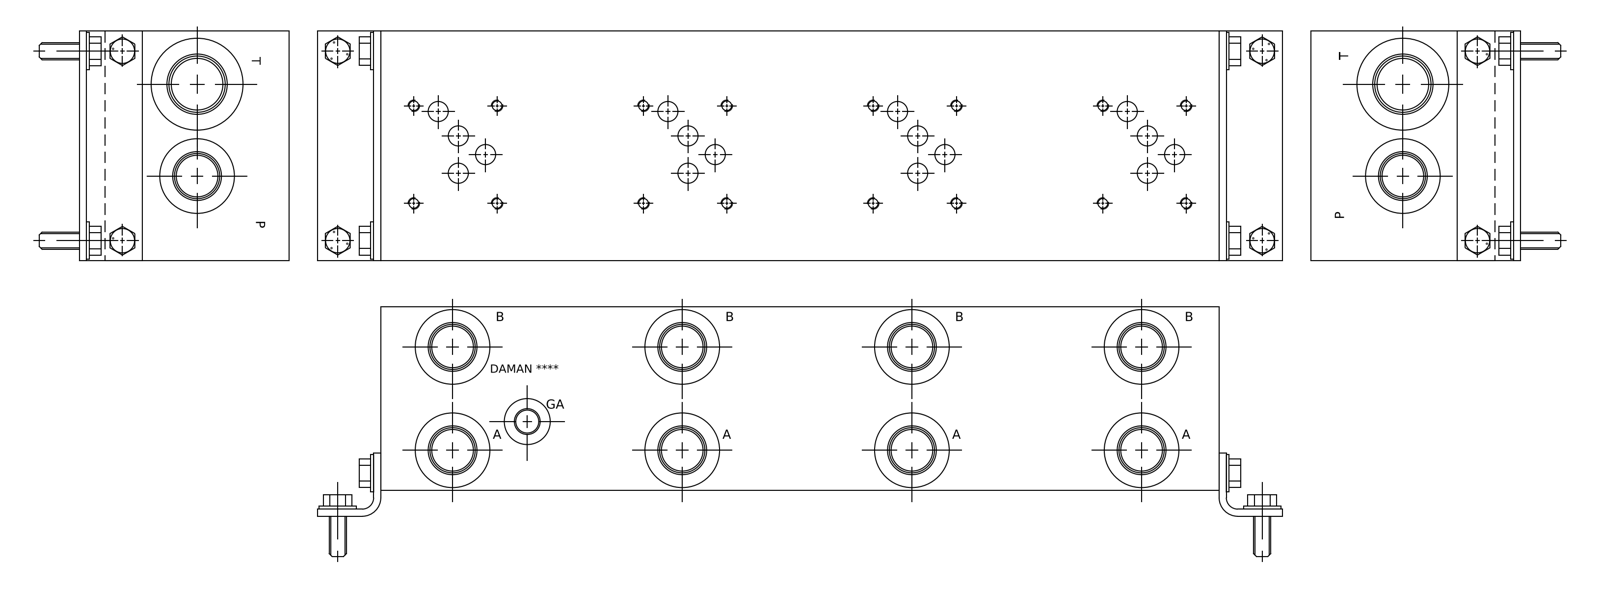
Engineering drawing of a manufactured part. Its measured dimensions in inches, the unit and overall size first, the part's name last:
Units: inches
Overall size (bounding box): 18.25 × 5 × 4
Round holes (diameter × count): ⌀0.201 ×16, ⌀0.25 ×16, ⌀0.438 ×14, ⌀0.906 ×9, ⌀0.981 ×9, ⌀1.08 ×9, ⌀1.655 ×9, ⌀1.063 ×8, ⌀0.312 ×2, ⌀0.375 ×2, ⌀0.437 ×2, ⌀1.063 ×2
Main face-to-face distances: 4, 5, 18.25, 0.031, 4.969, 18.219, 18.188, 0.75, 0.781, 4.219
Hole centre spacings: 5, 10, 15, 2.793, 10, 0.72, 1.813, 5
Volume: 348.7 in³ · Surface area: 438.8 in²
Bodies: 1 solid, 829 faces (441 planar, 122 cylindrical, 266 other)
Part name (STEP PRODUCT): Part_AD05HP045S_3D
STEP written by: Autodesk Inventor 2020 (AUTOMOTIVE_DESIGN)
